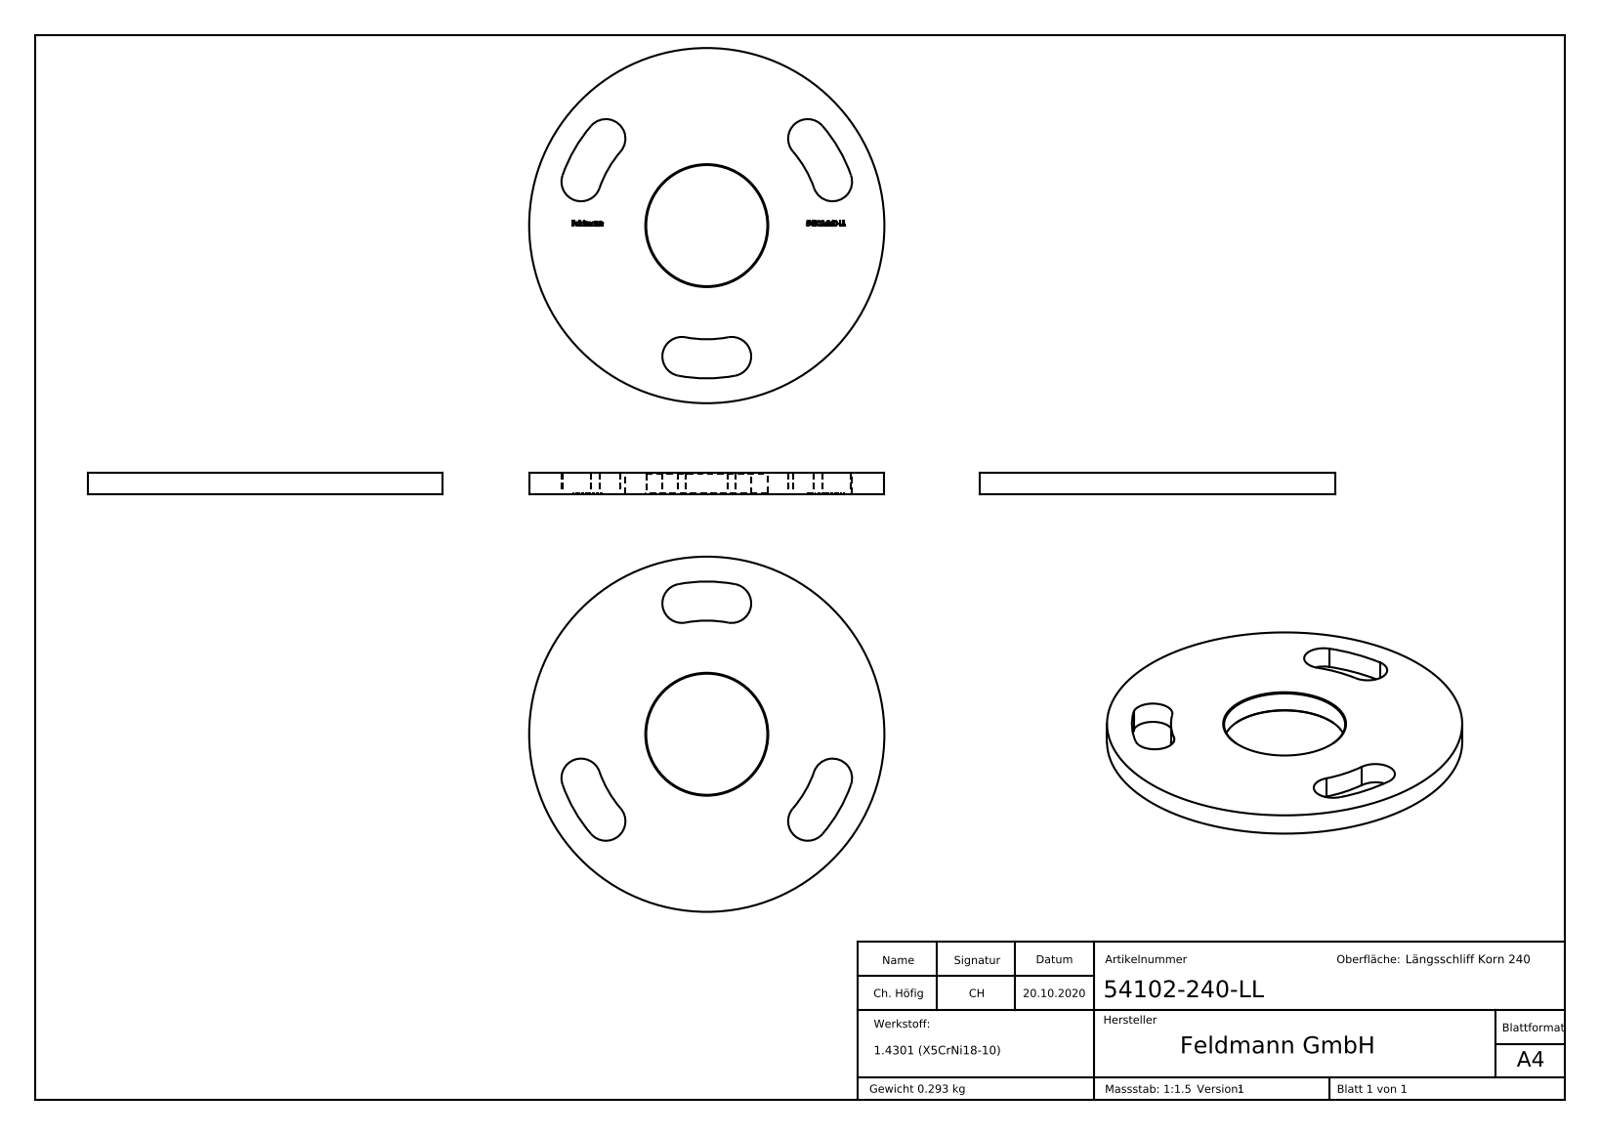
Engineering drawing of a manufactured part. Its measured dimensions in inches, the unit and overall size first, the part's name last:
Units: inches
Overall size (bounding box): 3.937 × 3.937 × 0.236
Round holes (diameter × count): ⌀1.343 ×1
Round bosses / shafts (diameter × count): ⌀3.937 ×1
Partial cylindrical surfaces — rounded edges, fillets, slot ends (radius × count): R0.217 ×6, R1.26 ×1, R1.693 ×1
Main face-to-face distances: 0.236, 0.232, 0.017, 2.887, 0.08, 0.084, 2.882, 0.035, 2.609, 0.046
Volume: 2.266 in³ · Surface area: 24.83 in²
Bodies: 1 solid, 263 faces (153 planar, 20 cylindrical, 90 other)
Part name (STEP PRODUCT): 54102-240-LL
STEP written by: SolidWorks 2018 (CONFIG_CONTROL_DESIGN)
